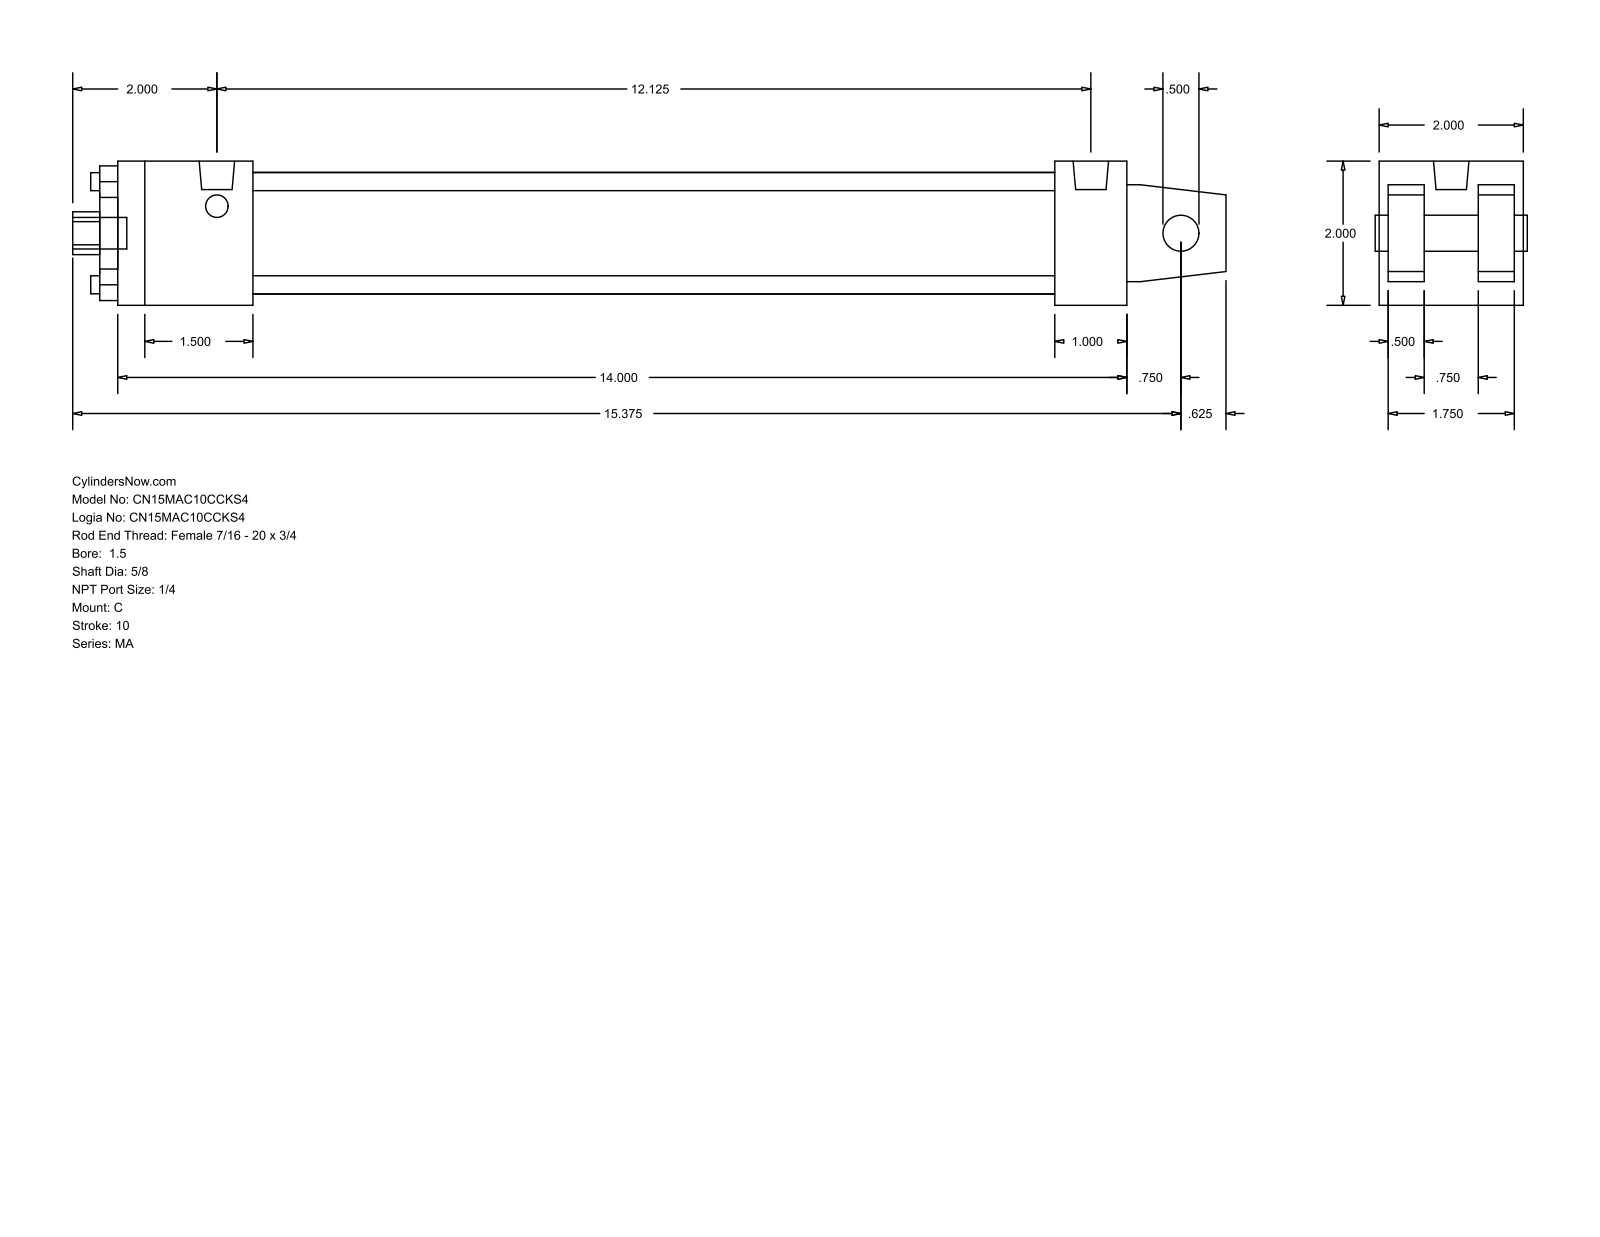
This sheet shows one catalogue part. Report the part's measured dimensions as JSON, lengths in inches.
{"part_name": "MA_C__0150_0.625", "step_written_by": "GSSL Pune (CONFIG_CONTROL_DESIGN)", "units": "inches", "bodies": {"solids": 0, "faces": 103, "planar": 76, "cylindrical": 27, "other": 0}, "overall_size": [16, 2, 2], "round_holes": [[0.25, 4], [0.5, 1], [0.625, 1], [1.125, 1], [1.69, 1]], "round_bosses_or_shafts": [[0.313, 4], [0.492, 2], [0.437, 1]], "partial_cylinders_radius": [[0.297, 1]], "face_to_face_distances": [2, 0.5, 0.125, 0.625, 1.375, 1.875, 1.25, 14, 13, 1], "hole_center_spacings": [1.011, 1.43, 2.022]}
